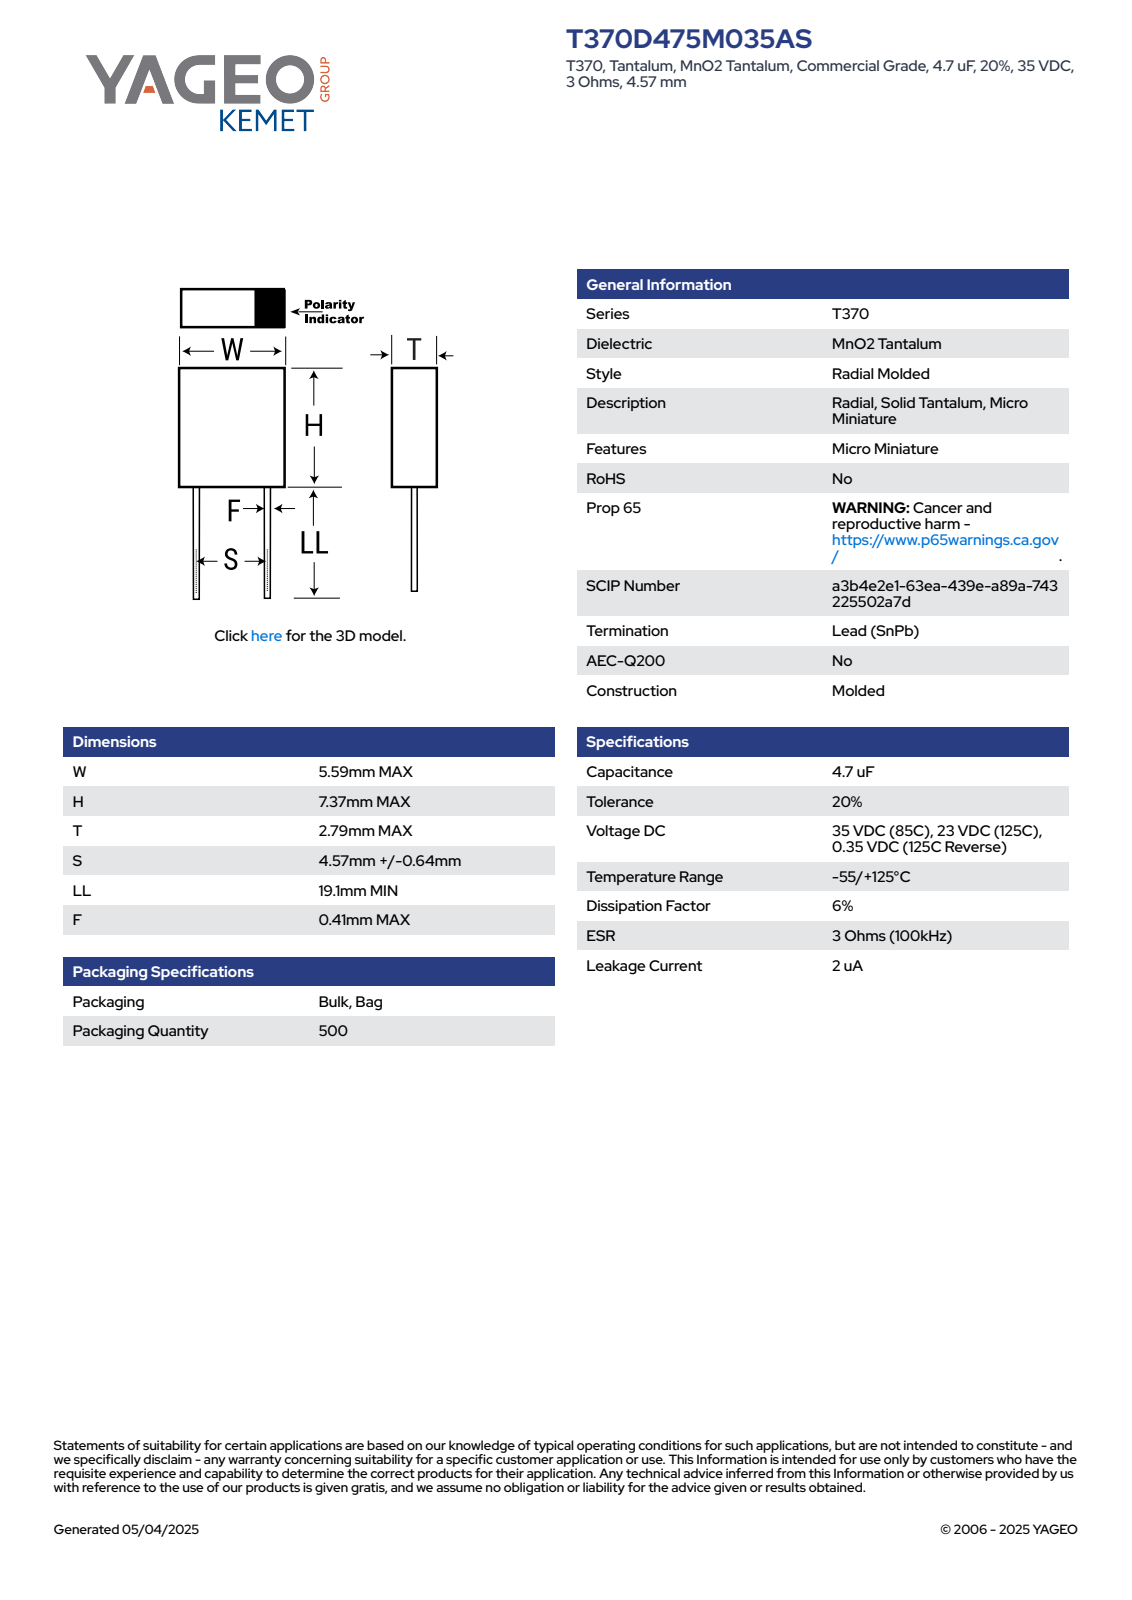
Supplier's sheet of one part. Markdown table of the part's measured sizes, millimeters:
| quantity | value |
| --- | --- |
| part name | CTR_T370_W5.59H7.37T2.79S4.57LL10.16F0.44 |
| STEP written by | SolidWorks 2014 (AUTOMOTIVE_DESIGN) |
| units | millimeters |
| bodies | 4 solids, 71 faces (67 planar, 4 cylindrical, 0 other) |
| overall size | 17.53 × 5.59 × 2.79 |
| volume | 118 mm³ |
| surface area | 188 mm² |
| round bosses / shafts (diameter × count) | 0.44 × 2 |
| main face-to-face distances | 2.79, 5.59, 7.37, 10.16, 17.53, 0.89, 14.4, 4.24, 3.13, 13.51 |
